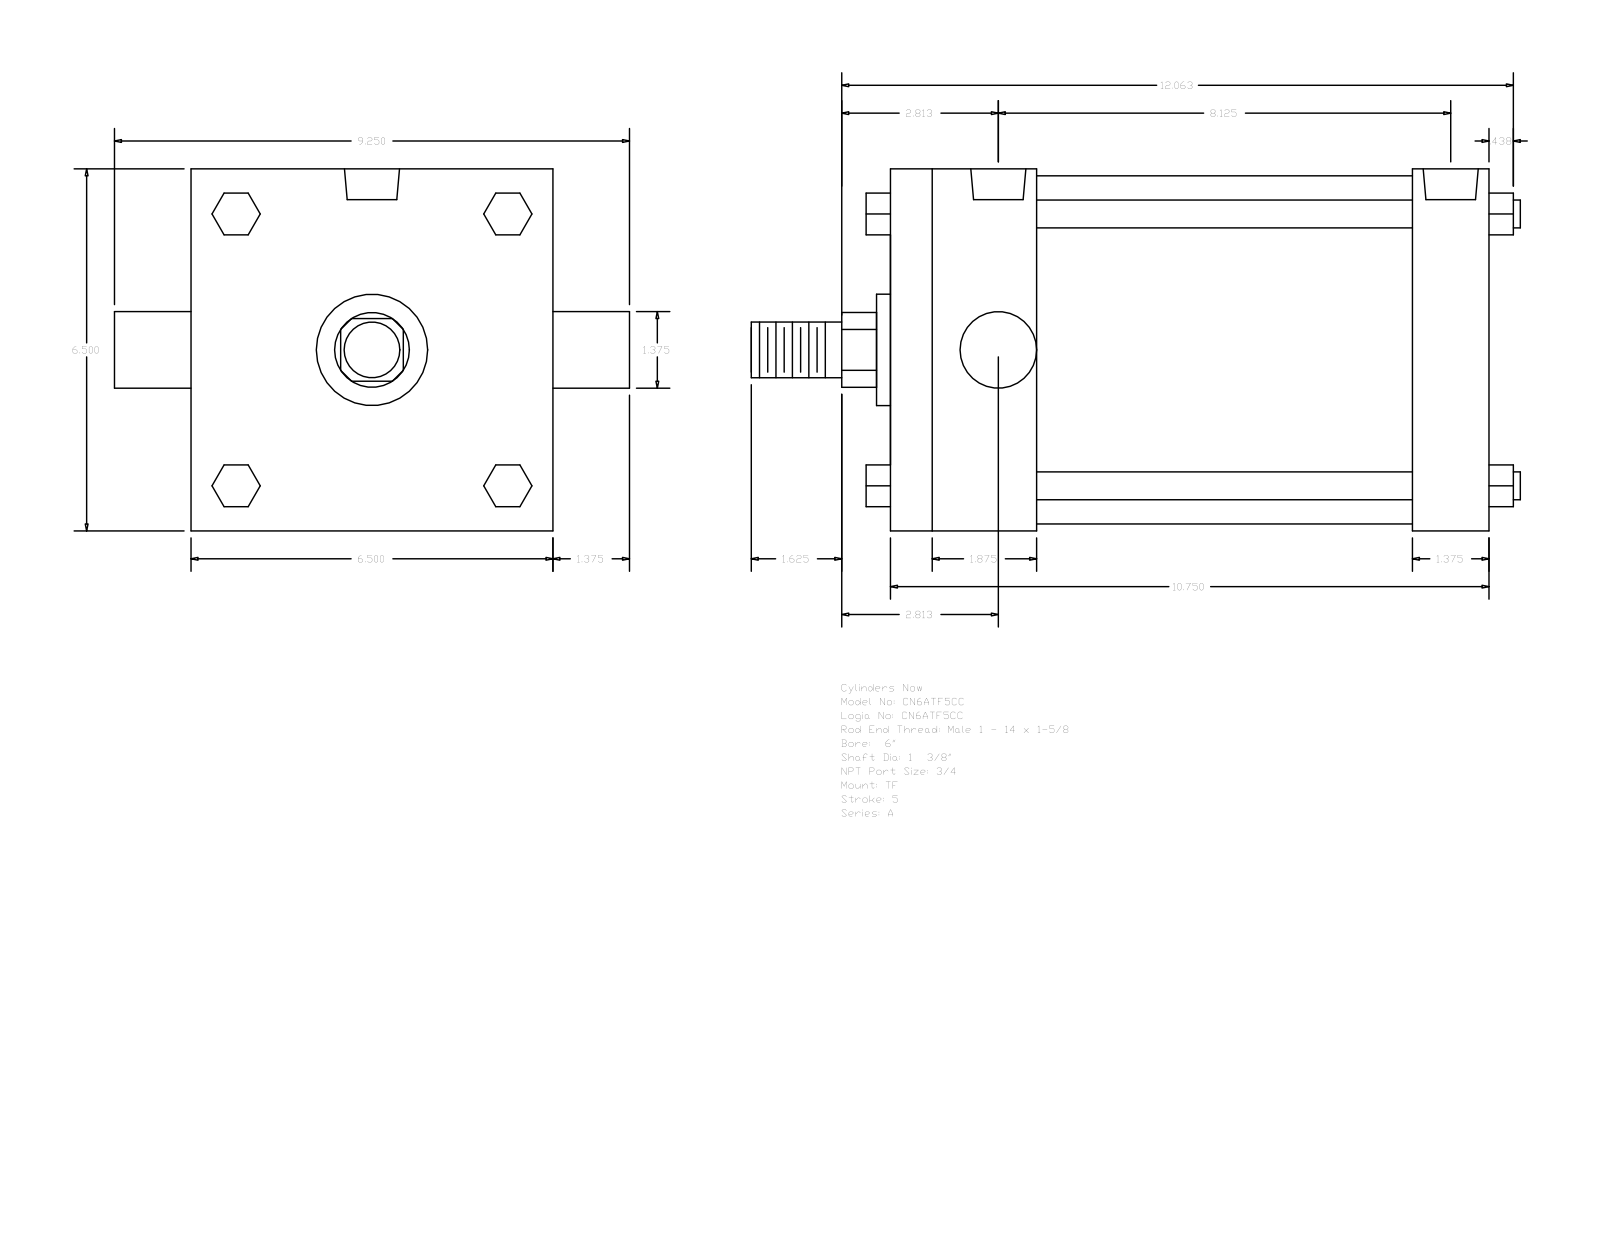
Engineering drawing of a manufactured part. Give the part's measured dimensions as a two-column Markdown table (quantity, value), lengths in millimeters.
| quantity | value |
| --- | --- |
| part name | A_TF__0600_1.375 |
| STEP written by | GSSL Pune (CONFIG_CONTROL_DESIGN) |
| units | millimeters |
| bodies | 0 solids, 120 faces (92 planar, 28 cylindrical, 0 other) |
| overall size | 350.84 × 234.95 × 165.1 |
| round holes (diameter × count) | 15.08 × 3, 25.12 × 2 |
| round bosses / shafts (diameter × count) | 12.7 × 4, 34.92 × 2, 158.75 × 1, 50.8 × 1, 25.4 × 1 |
| partial cylindrical surfaces (radius × count) | 17.06 × 1 |
| main face-to-face distances | 165.1, 273.04, 34.92, 66.67, 206.37, 238.12, 171.45, 19.05, 61.97, 107.34 |
| hole center spacings | 5.56, 200.81, 195.25, 206.37 |
